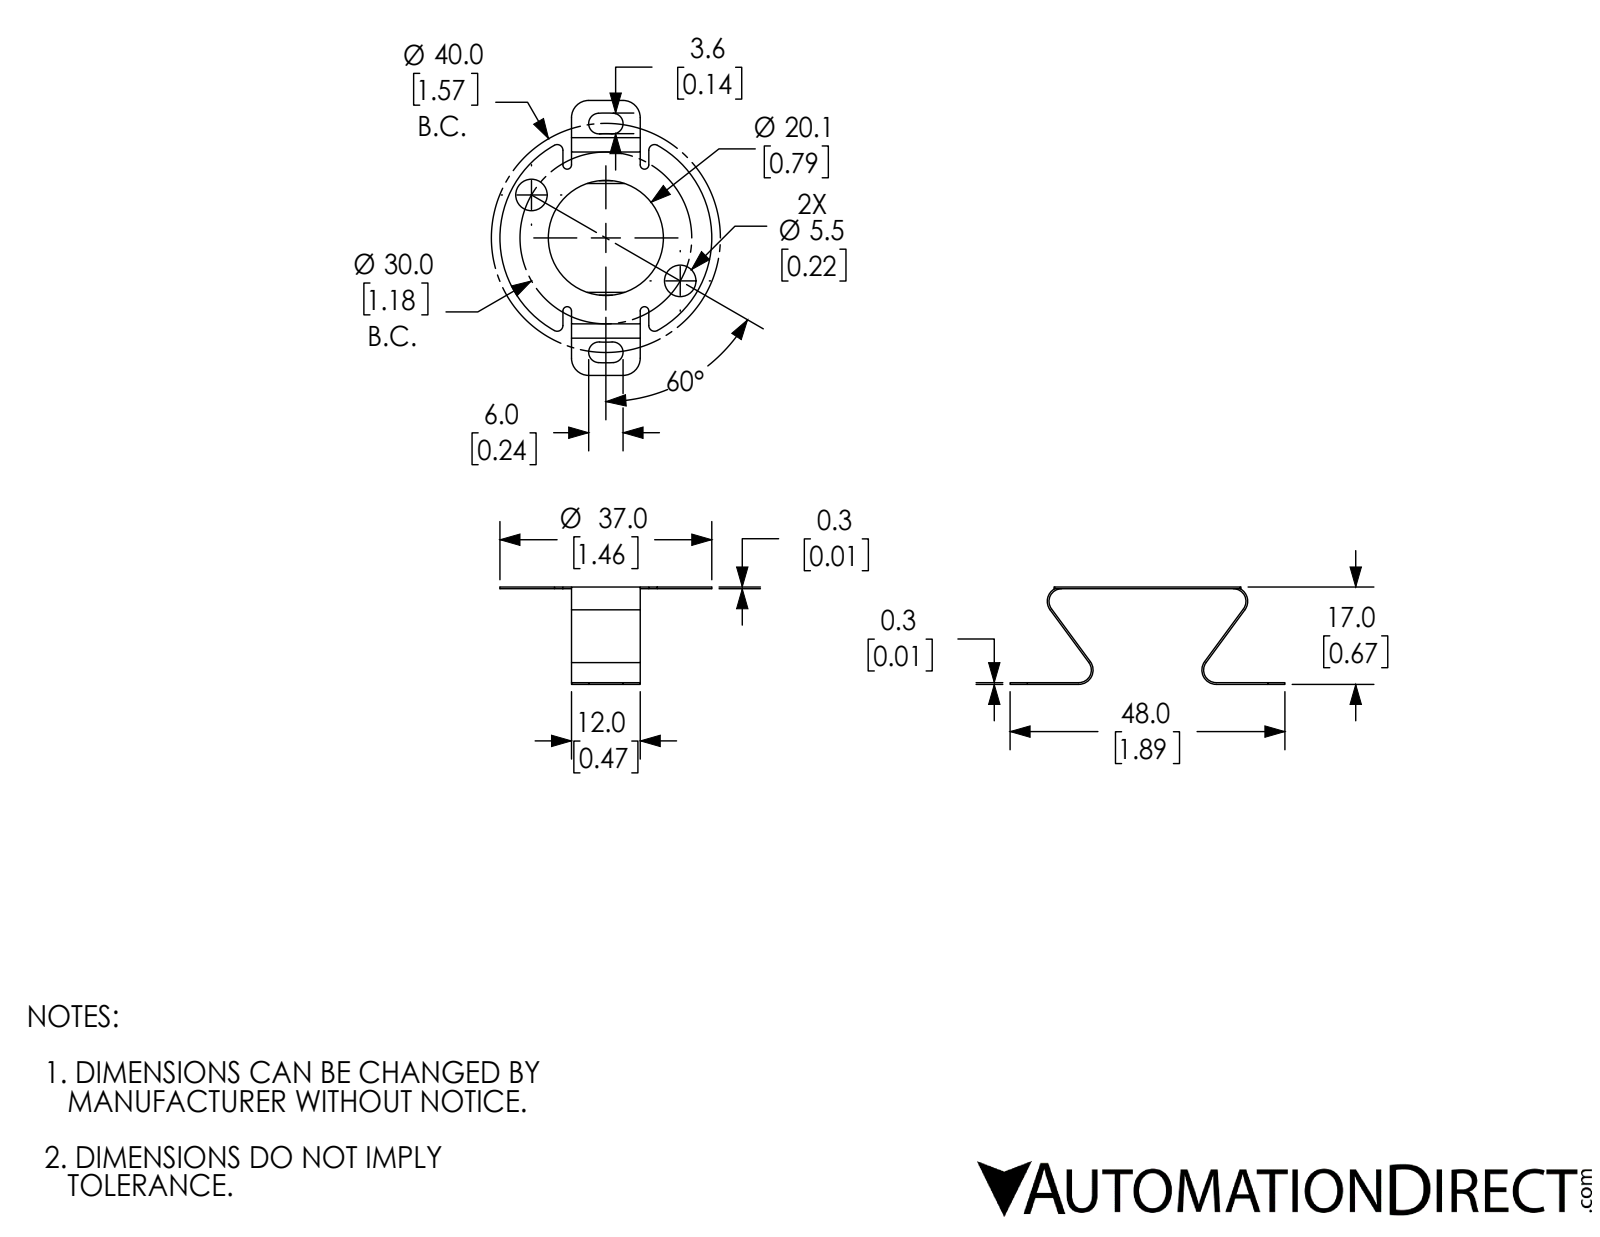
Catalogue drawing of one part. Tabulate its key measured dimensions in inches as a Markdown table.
| quantity | value |
| --- | --- |
| part name | TRD-SHRW-40 |
| STEP written by | SolidWorks 2017 (AUTOMOTIVE_DESIGN) |
| units | inches |
| bodies | 1 solid, 70 faces (20 planar, 50 cylindrical, 0 other) |
| overall size | 1.89 × 1.457 × 0.669 |
| volume | 0.025 in³ |
| surface area | 4.425 in² |
| round holes (diameter × count) | 0.217 × 2, 0.791 × 1 |
| partial cylindrical surfaces (radius × count) | 0.03 × 4, 0.039 × 4, 0.071 × 4, 0.087 × 4, 0.098 × 4, 0.118 × 4, 0.717 × 1, 0.728 × 1 |
| main face-to-face distances | 0.657, 0.646, 0.669, 0.472, 0.059, 0.531, 1.89, 0.591 |
| hole center spacings | 0.591, 1.181 |
